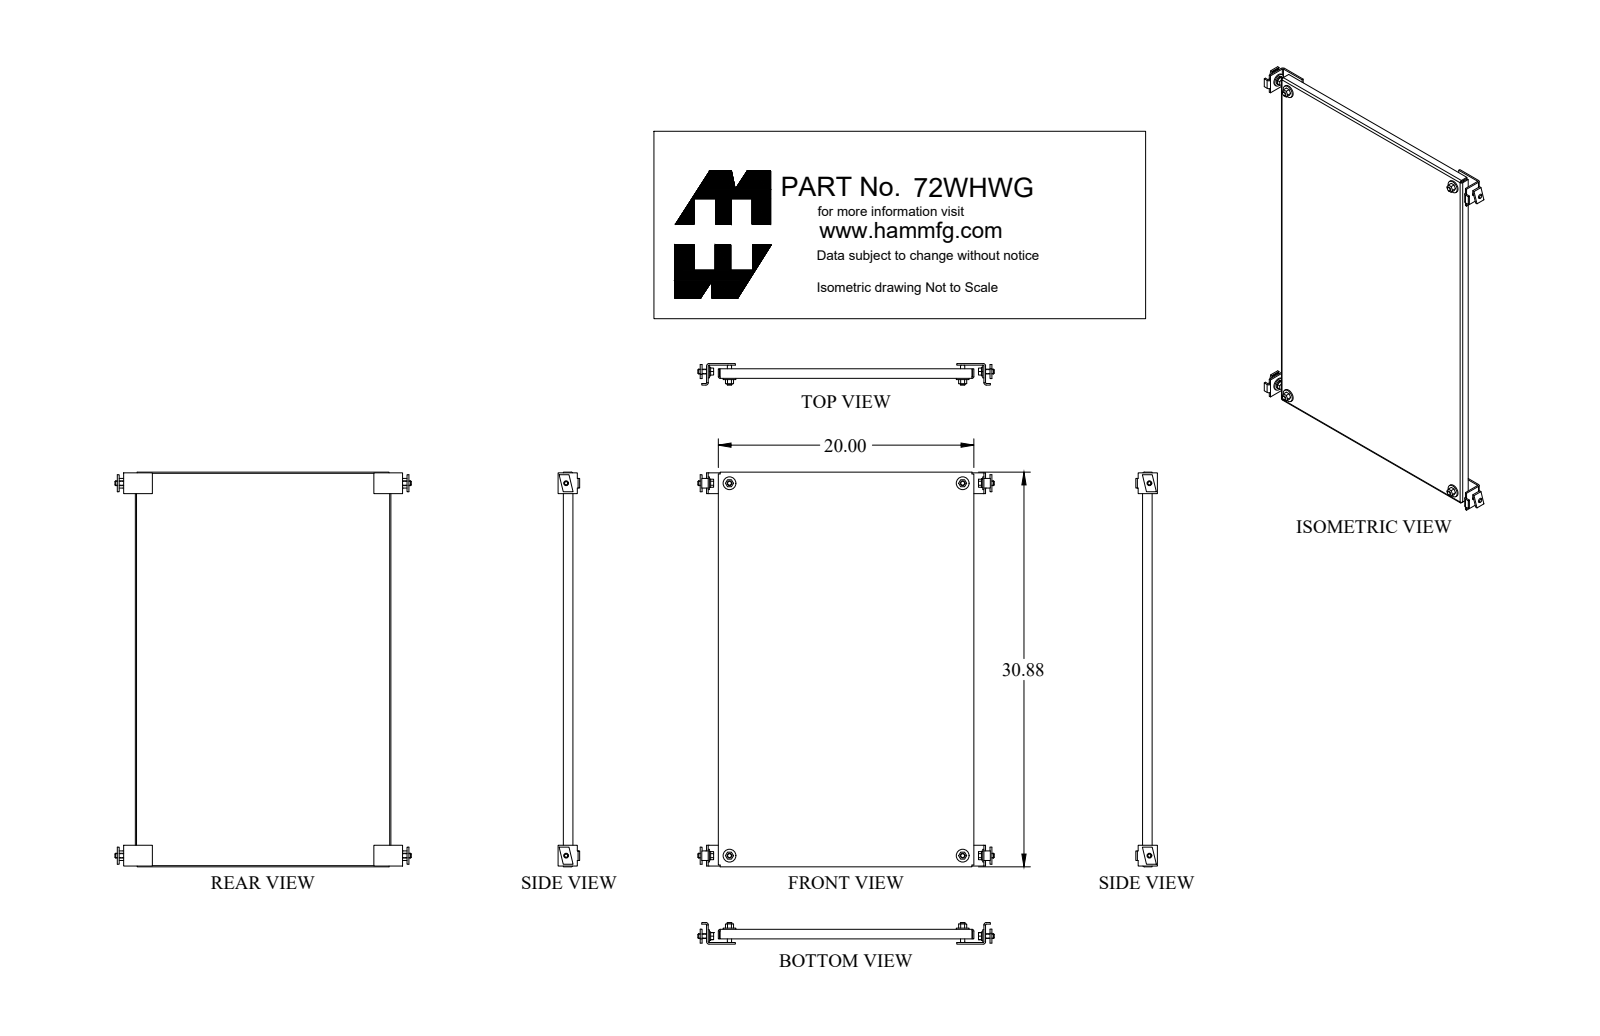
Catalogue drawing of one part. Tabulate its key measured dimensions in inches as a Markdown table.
| quantity | value |
| --- | --- |
| part name | 72WHWG_Default |
| STEP written by | SolidWorks 2018 (CONFIG_CONTROL_DESIGN) |
| units | inches |
| bodies | 9 solids, 190 faces (94 planar, 64 cylindrical, 32 other) |
| overall size | 30.875 × 22.582 × 1.687 |
| volume | 68.13 in³ |
| surface area | 1 431 in² |
| round holes (diameter × count) | 0.563 × 4, 0.437 × 2 |
| round bosses / shafts (diameter × count) | 0.65 × 4, 0.375 × 4, 0.33 × 4 |
| partial cylindrical surfaces (radius × count) | 0.048 × 4, 0.06 × 4, 0.143 × 4, 0.185 × 4 |
| main face-to-face distances | 0.095, 19.905, 30.78, 0.125, 19.81, 20, 1.032, 0.937, 1.157, 1.062 |
| hole center spacings | 18.25, 29.125, 34.37, 29.13 |
